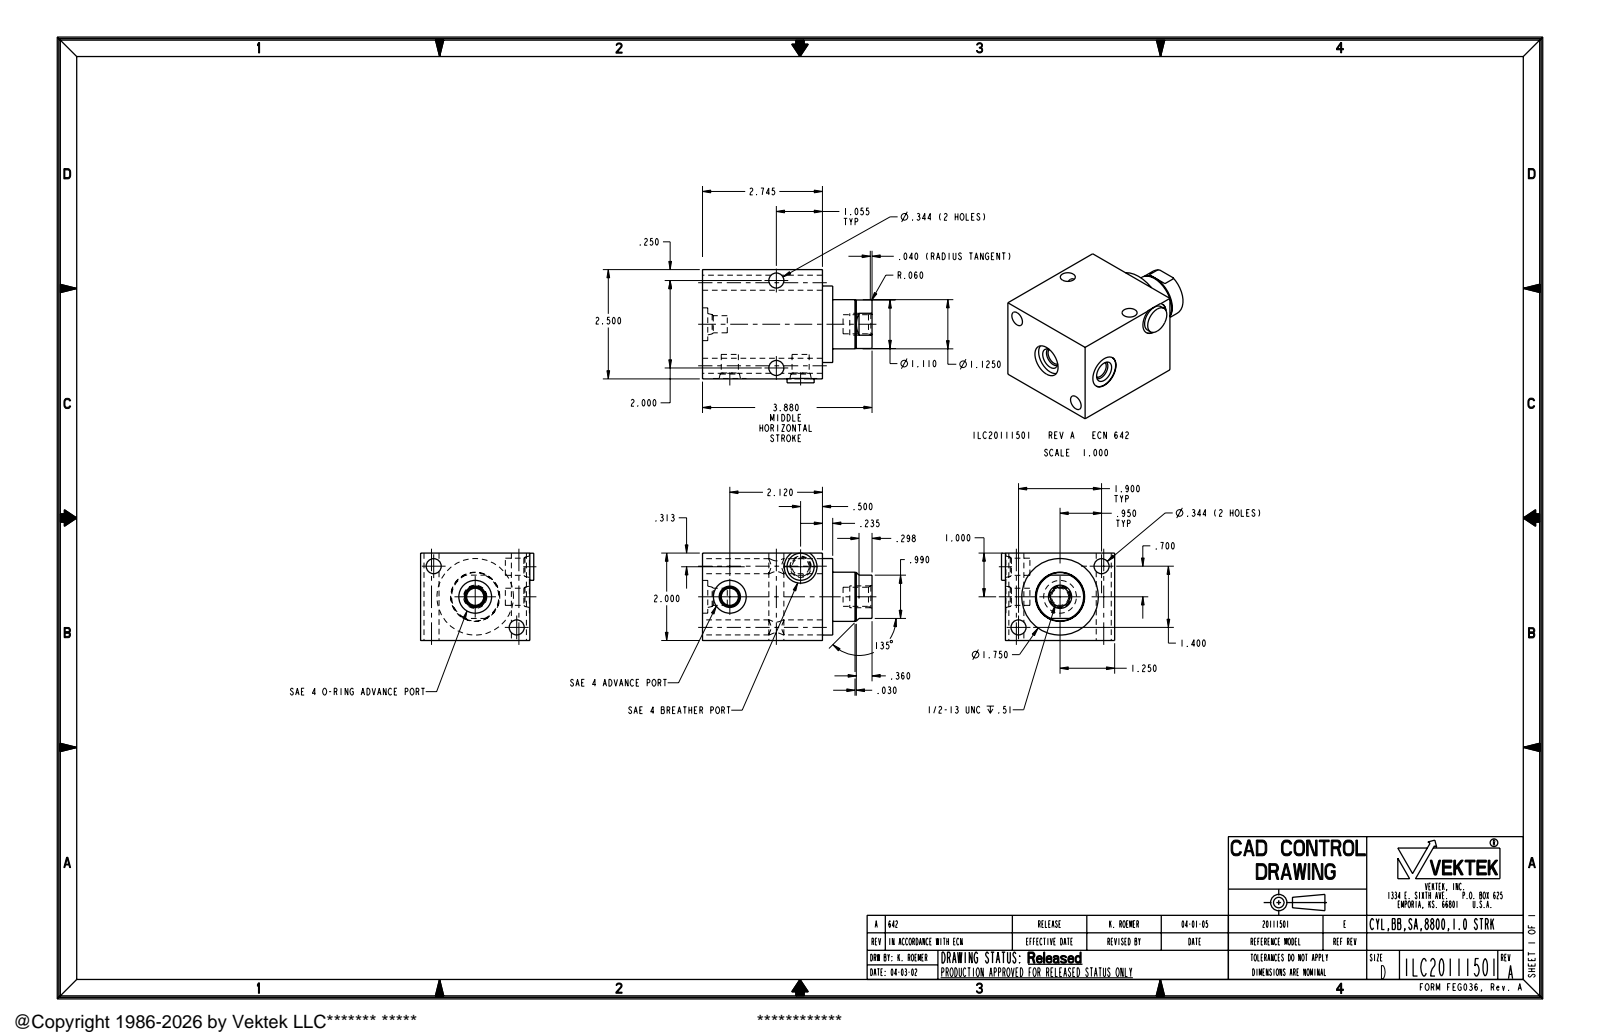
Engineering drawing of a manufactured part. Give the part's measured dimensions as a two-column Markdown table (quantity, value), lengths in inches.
| quantity | value |
| --- | --- |
| part name | ILC20111501 |
| STEP written by | PRO/ENGINEER BY PARAMETRIC TECHNOLOGY CORPORATION, 2004290 (AUTOMOTIVE_DESIGN_CC2) |
| units | inches |
| bodies | 1 solid, 75 faces (22 planar, 35 cylindrical, 18 other) |
| overall size | 3.88 × 2.59 × 2 |
| volume | 13.99 in³ |
| surface area | 52.08 in² |
| round holes (diameter × count) | 0.344 × 4, 0.392 × 3, 0.75 × 3, 0.437 × 1 |
| round bosses / shafts (diameter × count) | 1.75 × 1, 1.125 × 1, 1.11 × 1, 0.62 × 1, 0.5 × 1 |
| main face-to-face distances | 2, 2.5, 2.745, 0.235, 2.98, 0.9, 1.135, 3.88, 2.49, 0.09 |
| hole center spacings | 1.18, 1.76, 2, 2.36 |
